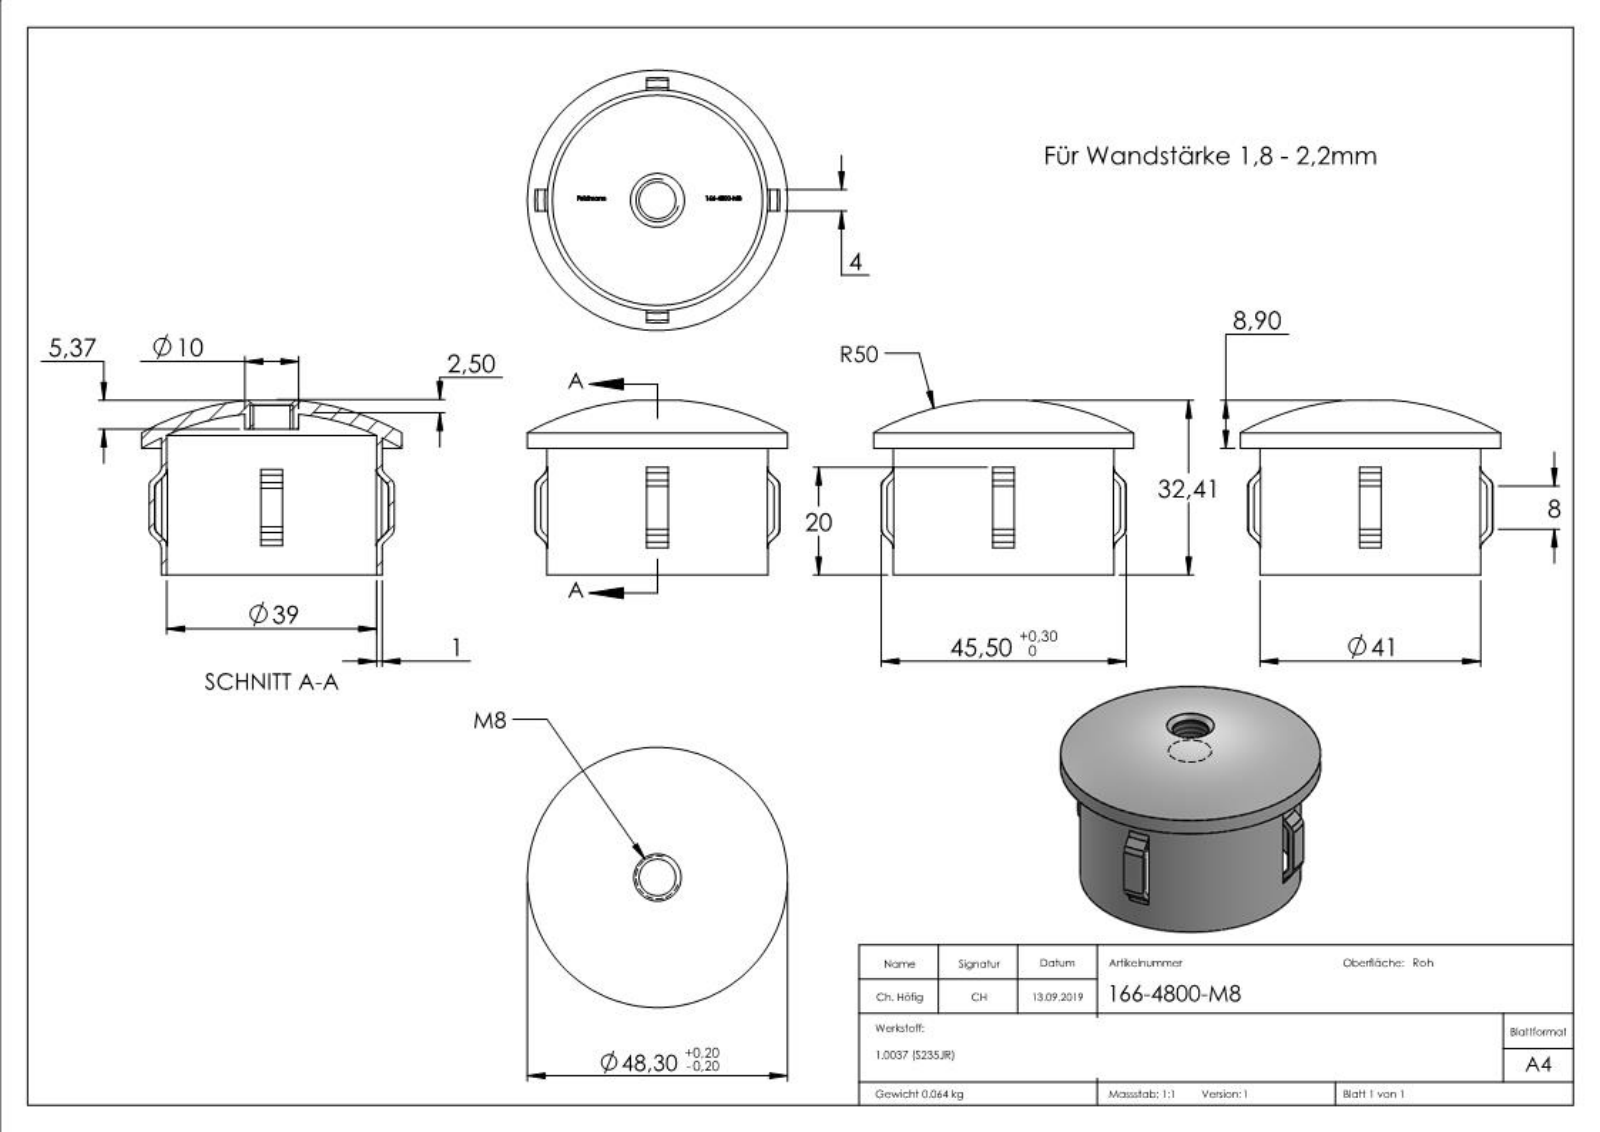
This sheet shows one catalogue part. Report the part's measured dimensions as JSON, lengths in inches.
{"part_name": "166-4800-M8", "step_written_by": "SolidWorks 2015 (CONFIG_CONTROL_DESIGN)", "units": "inches", "bodies": {"solids": 1, "faces": 372, "planar": 118, "cylindrical": 20, "other": 234}, "overall_size": [1.902, 1.902, 1.276], "volume_in3": 0.499, "surface_area_in2": 17.34, "round_holes": [[0.268, 1], [1.535, 1]], "round_bosses_or_shafts": [[1.902, 1], [1.614, 1], [0.394, 1]], "partial_cylinders_radius": [[0.856, 1], [0.896, 1]], "face_to_face_distances": [0.157, 1.064, 0.079, 0.07, 0.048, 0.033, 0.039, 0.898, 0.089, 0.017]}
